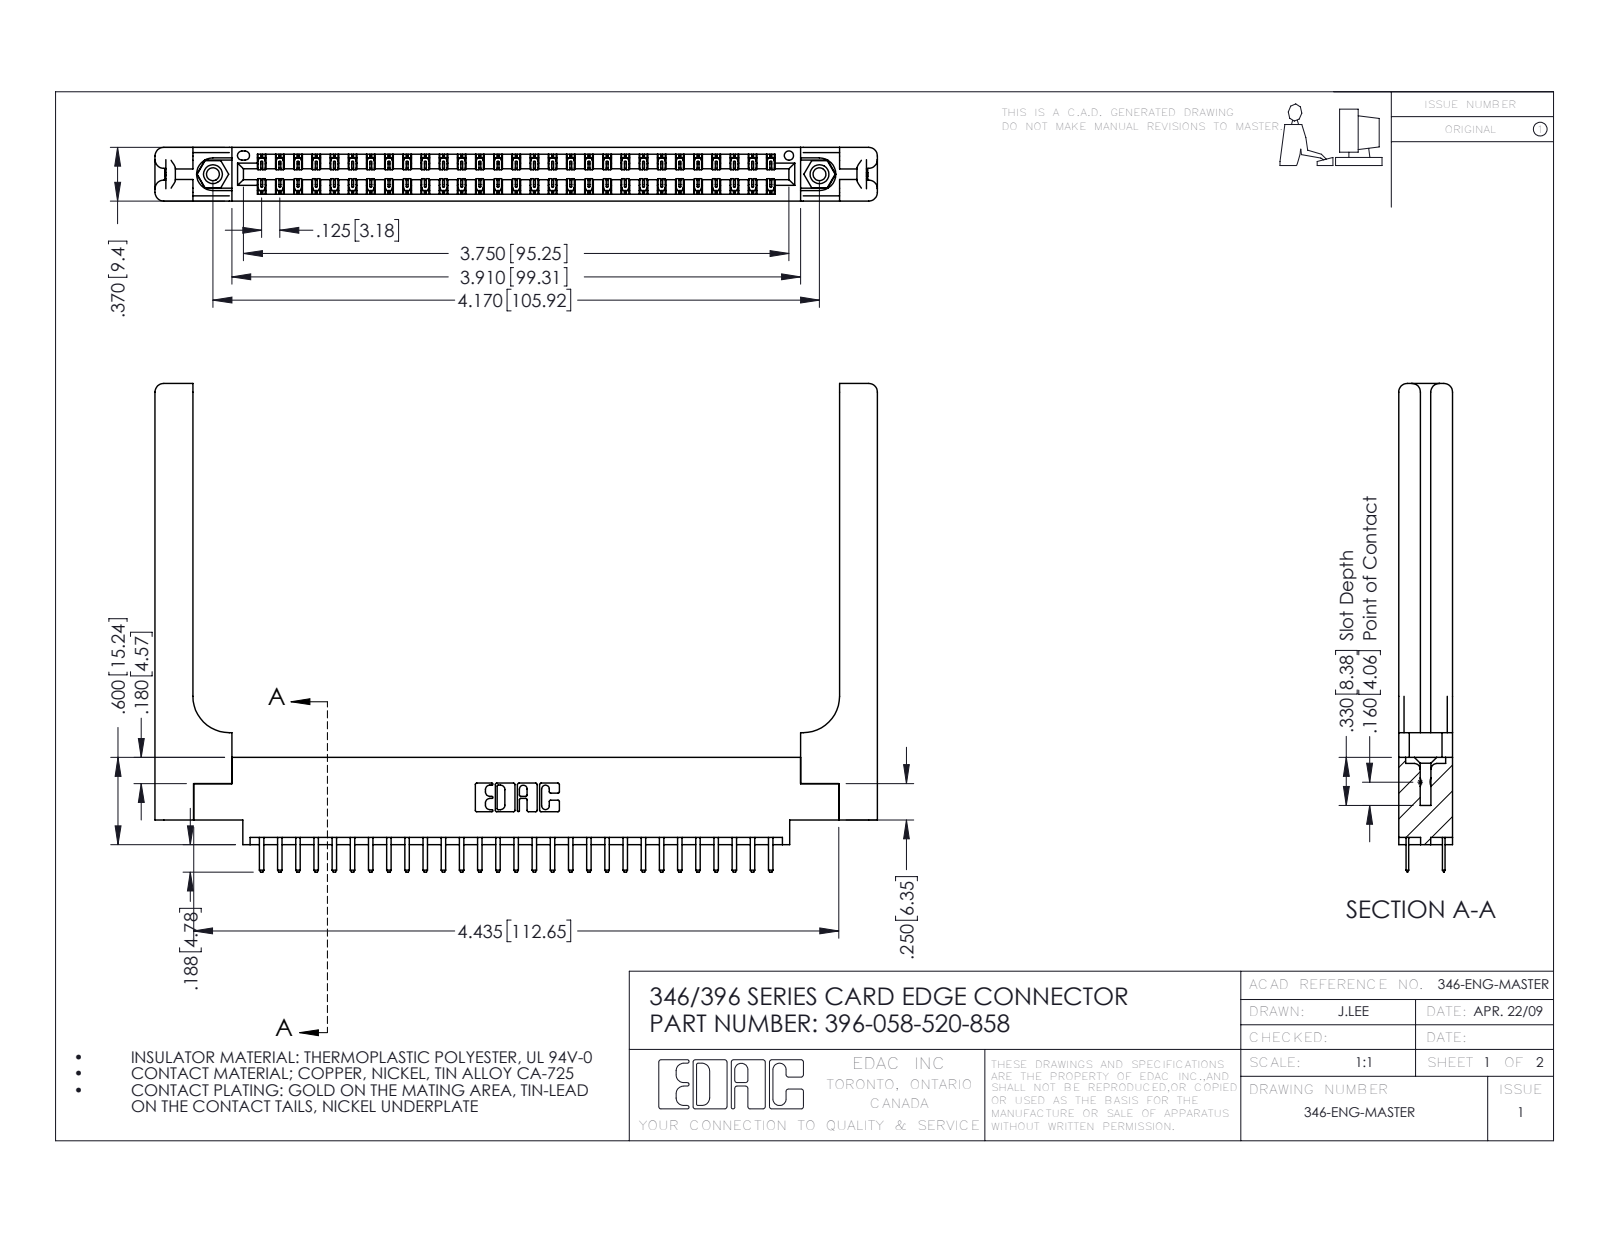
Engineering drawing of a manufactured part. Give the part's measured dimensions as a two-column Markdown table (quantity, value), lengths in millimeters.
| quantity | value |
| --- | --- |
| part name | 345-292-001_345-293-120; 346 Part_0.170 Offset - 0.156 Dia-TH; 346-220-058_345-220-058; 396-058-520-858 (+1 more) |
| STEP written by | SolidWorks 2016 (CONFIG_CONTROL_DESIGN) |
| units | millimeters |
| bodies | 63 solids, 3630 faces (2374 planar, 1196 cylindrical, 60 other) |
| overall size | 126.1 × 85.3 × 9.4 |
| volume | 19 520 mm³ |
| surface area | 21 410 mm² |
| round holes (diameter × count) | 2.3 × 2, 3.2 × 2, 4 × 2, 1.6 × 1 |
| round bosses / shafts (diameter × count) | 3.9 × 2 |
| partial cylindrical surfaces (radius × count) | 0.2 × 87, 0.3 × 62, 0.3 × 22, 1.5 × 16, 0.2 × 6, 0.8 × 6, 0.7 × 3, 0.4 × 2 |
| main face-to-face distances | 9.4, 1.2, 8.2, 1.8, 3.8, 3.8, 6.4, 7.6, 0.6, 7 |
| hole center spacings | 6.2, 100.6, 105.9 |
